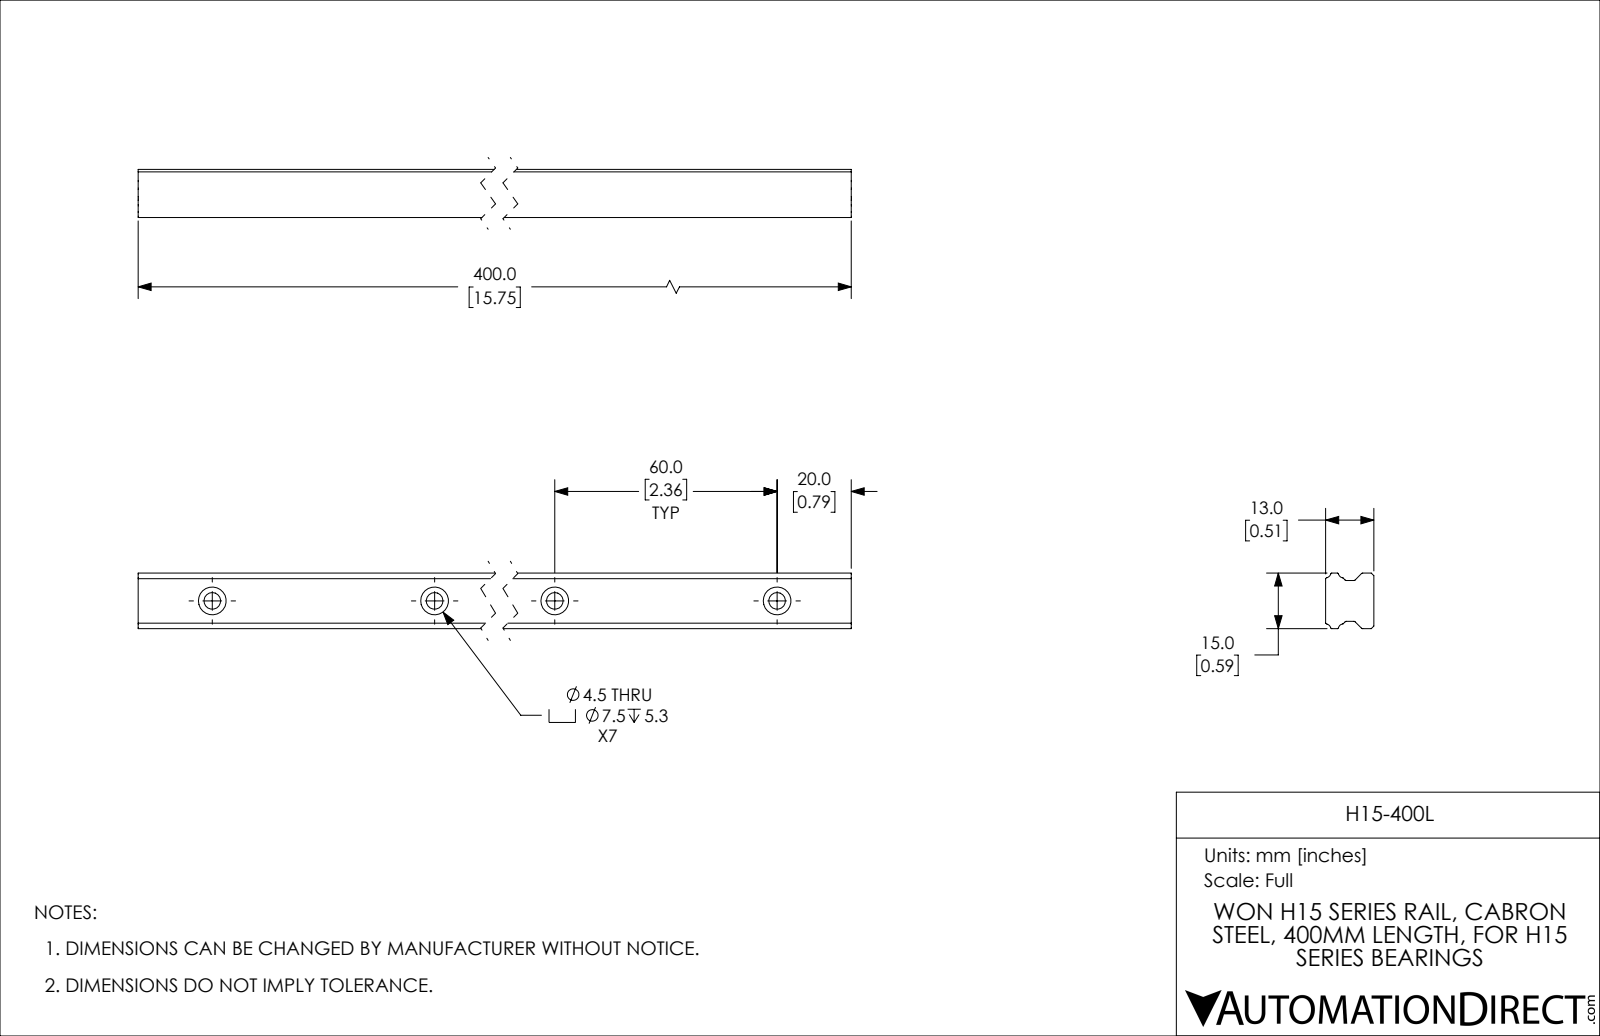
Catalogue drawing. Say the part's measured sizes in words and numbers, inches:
The part is named "H15-400L". Its 3-D file was written by "SolidWorks 2019 (CONFIG_CONTROL_DESIGN)". It is 1 solid with 69 faces: 23 planar, 46 cylindrical and 0 other. Overall it measures 15.748 by 0.591 by 0.512 inches. Its volume is 4.077 cubic inches and its surface area 38 square inches. Round holes: 7 of diameter 0.177, 7 of diameter 0.295. Partial cylindrical surfaces (rounded edges, fillets, slot ends): 6 of radius 0.012, 6 of radius 0.02, 4 of radius 0.055, 2 of radius 0.024. The main face-to-face distances are 0.512, 0.079, 0.591, 0.433, 0.487, 0.239, 0.248, 0.303, 0.209, 15.748. The hole center spacings are 2.362, 4.724, 7.087, 9.449, 11.811, 14.173.
